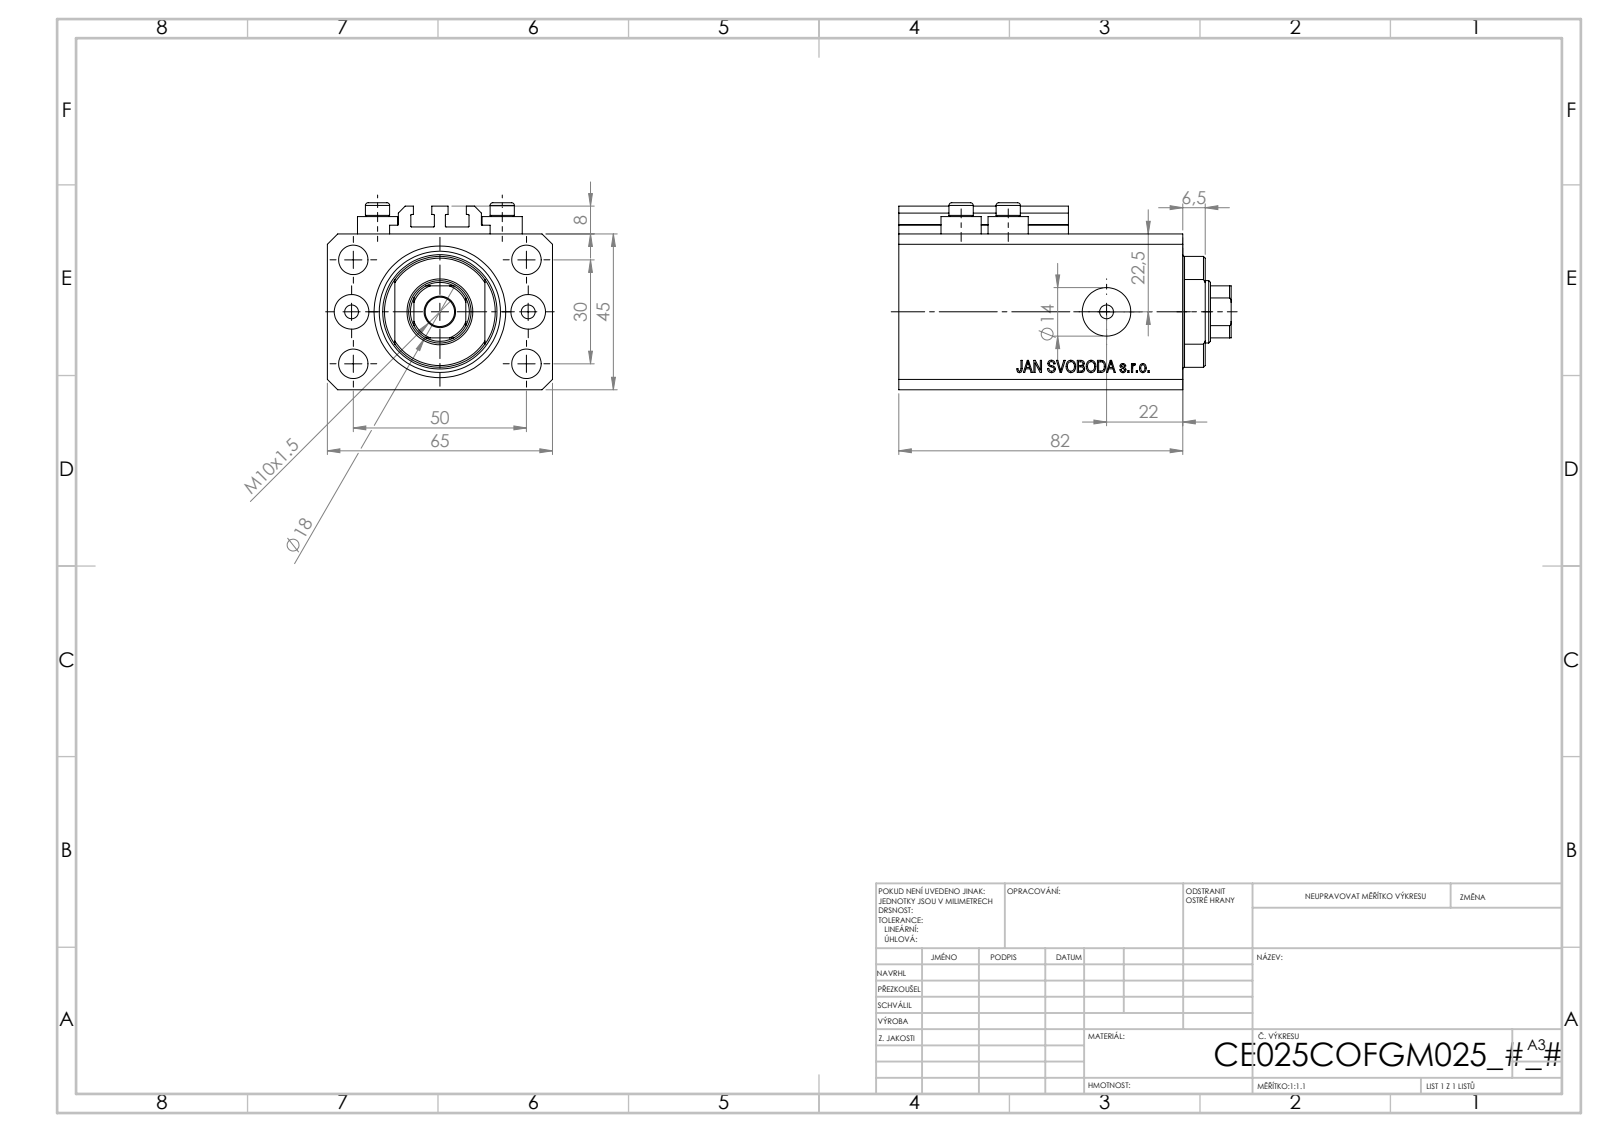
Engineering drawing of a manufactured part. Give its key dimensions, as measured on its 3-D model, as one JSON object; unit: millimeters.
{"part_name": "ALLEN BOLT V250CE; V250CE_C_VCP; V250CE_C_Body; V250CE_VC_C", "step_written_by": "SolidWorks 2019 (CONFIG_CONTROL_DESIGN)", "units": "millimeters", "bodies": {"solids": 8, "faces": 1034, "planar": 504, "cylindrical": 86, "other": 444}, "overall_size": [96, 65, 54], "volume_mm3": 224788, "surface_area_mm2": 60044, "round_holes": [[4, 8], [8.5, 5], [10, 2], [14, 2], [18, 1], [25, 1], [38, 1]], "round_bosses_or_shafts": [[11.6, 4], [7, 4]], "partial_cylinders_radius": [[0.2, 10], [8.5, 1], [16, 1]], "face_to_face_distances": [45, 65, 14, 68, 82, 47, 6.9, 61.1, 75.1, 3], "hole_center_spacings": [15.01, 29.15, 52.68, 13.6, 25.5, 30, 36, 38.48]}
